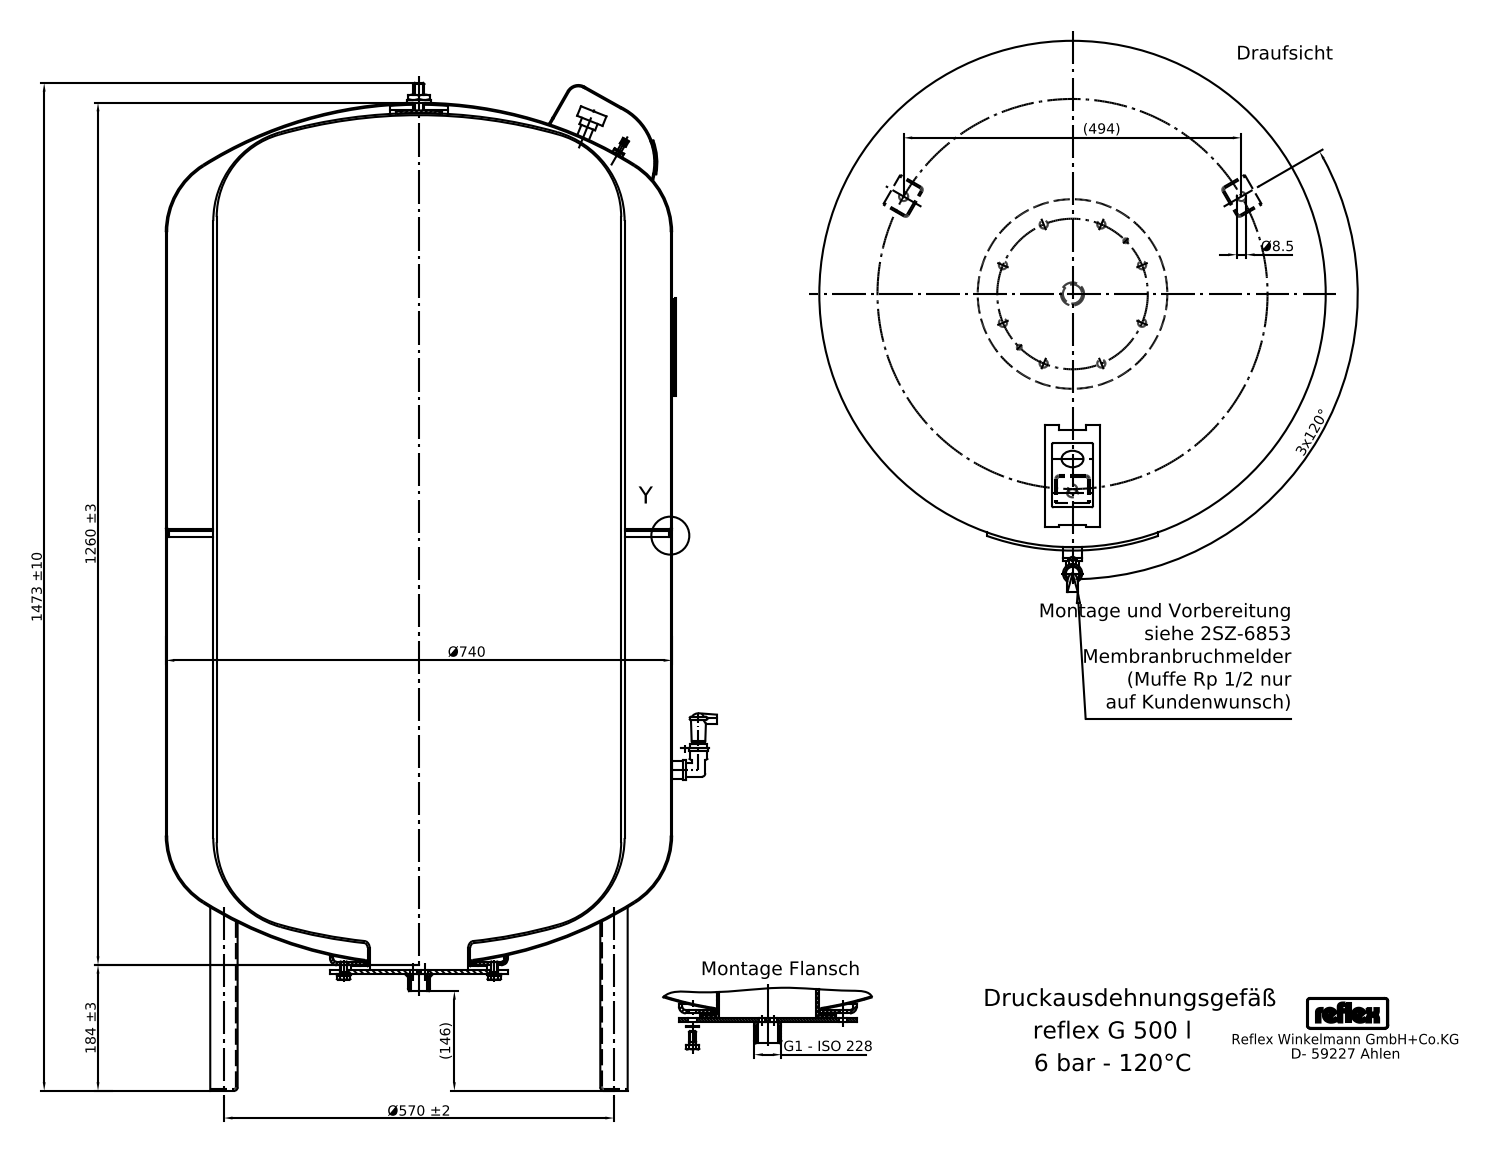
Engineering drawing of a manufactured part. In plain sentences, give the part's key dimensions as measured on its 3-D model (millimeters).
Its 3-D file was written by "Mechanical Desktop 2008 (CONFIG_CONTROL_DESIGN)". It is 21 solids with 505 faces: 229 planar, 183 cylindrical and 93 other. Overall it measures 1473 by 805 by 741.14 millimeters. Its volume is 487 100 000 cubic millimeters and its surface area 5 457 000 square millimeters. Round holes: 3 of diameter 13.4, 1 of diameter 2.48, 1 of diameter 7, 1 of diameter 8, 1 of diameter 10, 1 of diameter 11.4, 1 of diameter 161, 1 of diameter 250. Round bosses or shafts: 9 of diameter 10, 2 of diameter 28, 2 of diameter 26, 2 of diameter 20, 1 of diameter 740, 1 of diameter 260, 1 of diameter 230, 1 of diameter 62. Partial cylindrical surfaces (rounded edges, fillets, slot ends): 15 of radius 1, 15 of radius 2.5, 15 of radius 5, 4 of radius 3.94, 3 of radius 1.57, 2 of radius 2.69, 2 of radius 4.72, 2 of radius 6.49. The main face-to-face distances are 882, 2.5, 47.5, 196, 1078, 6, 202, 1084, 45, 50. The hole center spacings are 285, 493.64, 346.37, 385.5, 670.5.
